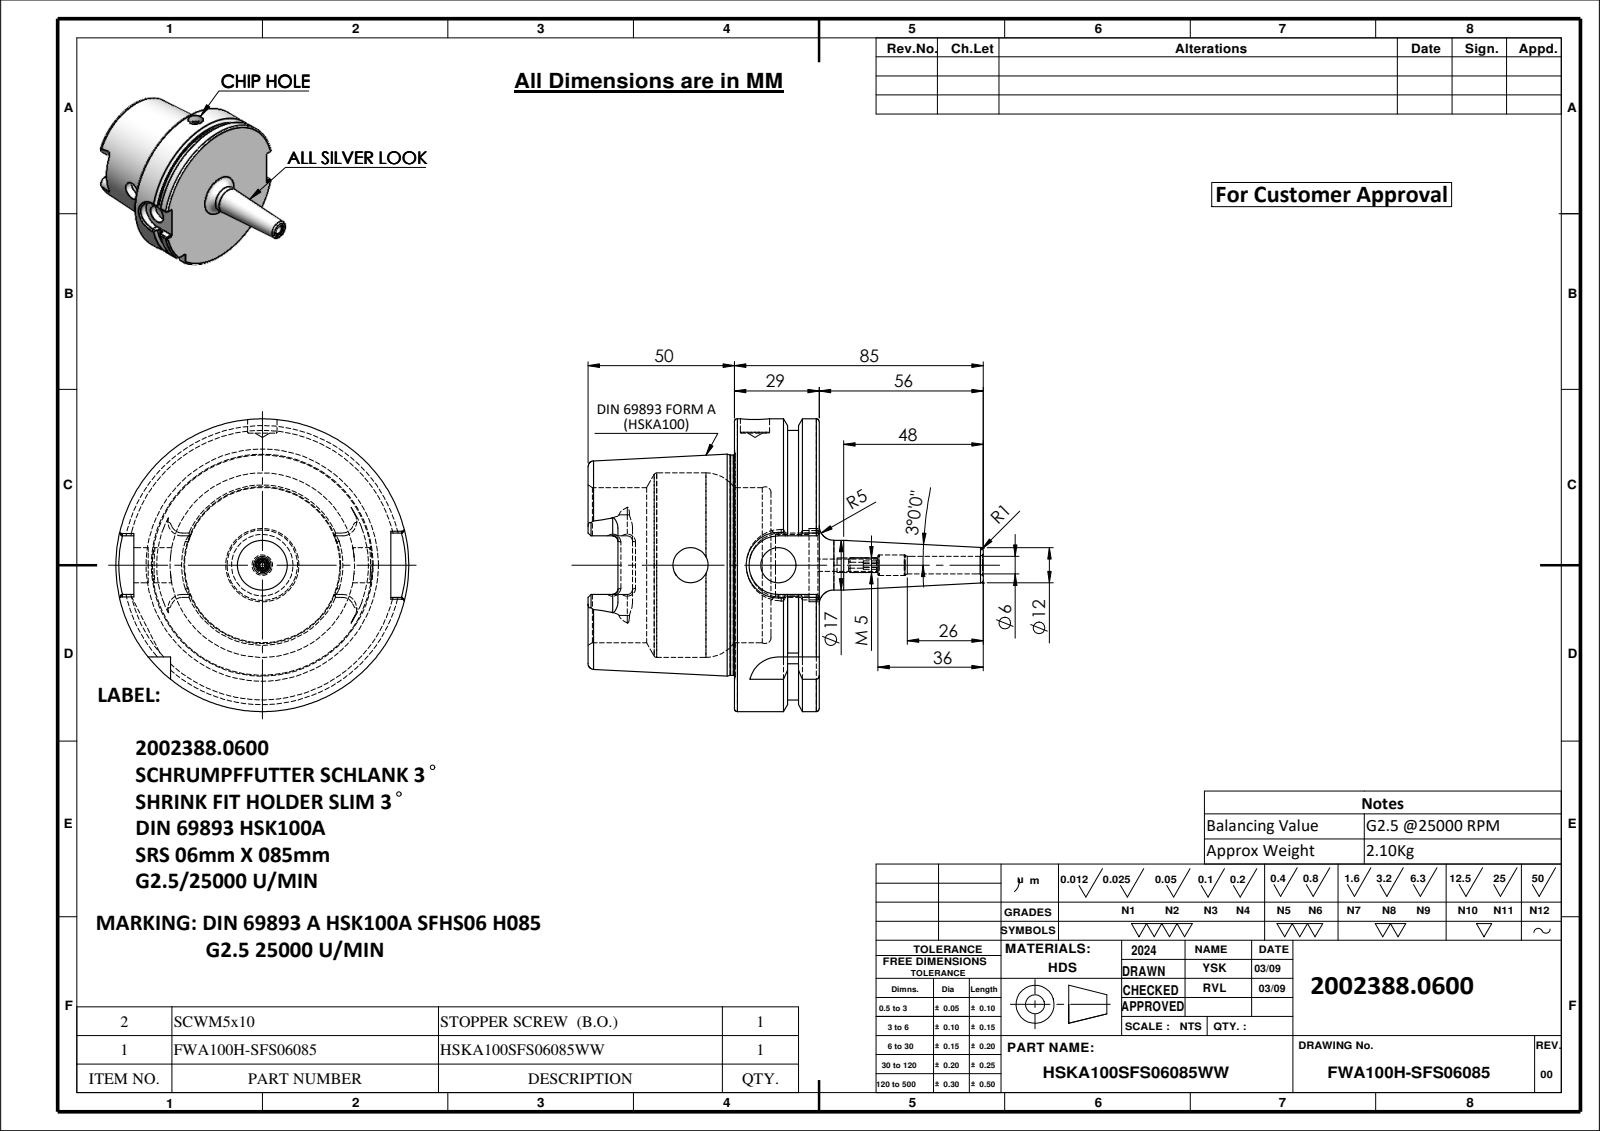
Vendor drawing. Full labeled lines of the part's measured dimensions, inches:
Part name (STEP PRODUCT): HSKA100SFS06085WW; SCWM5X10; FWA100H-SFS06085
STEP written by: SolidWorks 2024 (CONFIG_CONTROL_DESIGN)
Units: inches
Bodies: 2 solids, 207 faces (67 planar, 56 cylindrical, 84 other)
Overall size (bounding box): 5.315 × 3.937 × 3.937
Volume: 16.02 in³ · Surface area: 82.91 in²
Round holes (diameter × count): ⌀0.472 ×2, ⌀0.079 ×1, ⌀0.165 ×1, ⌀0.236 ×1, ⌀0.276 ×1, ⌀0.394 ×1, ⌀0.827 ×1, ⌀0.984 ×1, ⌀2.087 ×1, ⌀2.48 ×1
Round bosses / shafts (diameter × count): ⌀3.937 ×1, ⌀3.622 ×1, ⌀2.959 ×1, ⌀0.669 ×1, ⌀0.197 ×1
Partial cylindrical surfaces — rounded edges, fillets, slot ends (radius × count): R0.071 ×6, R0.192 ×4, R0.394 ×2, R0.433 ×1
Main face-to-face distances: 1.14, 0.492, 0.648, 1.969, 2.461, 3.108, 3.091, 1.122, 0.63, 0.018
Hole centre spacings: 1.181
